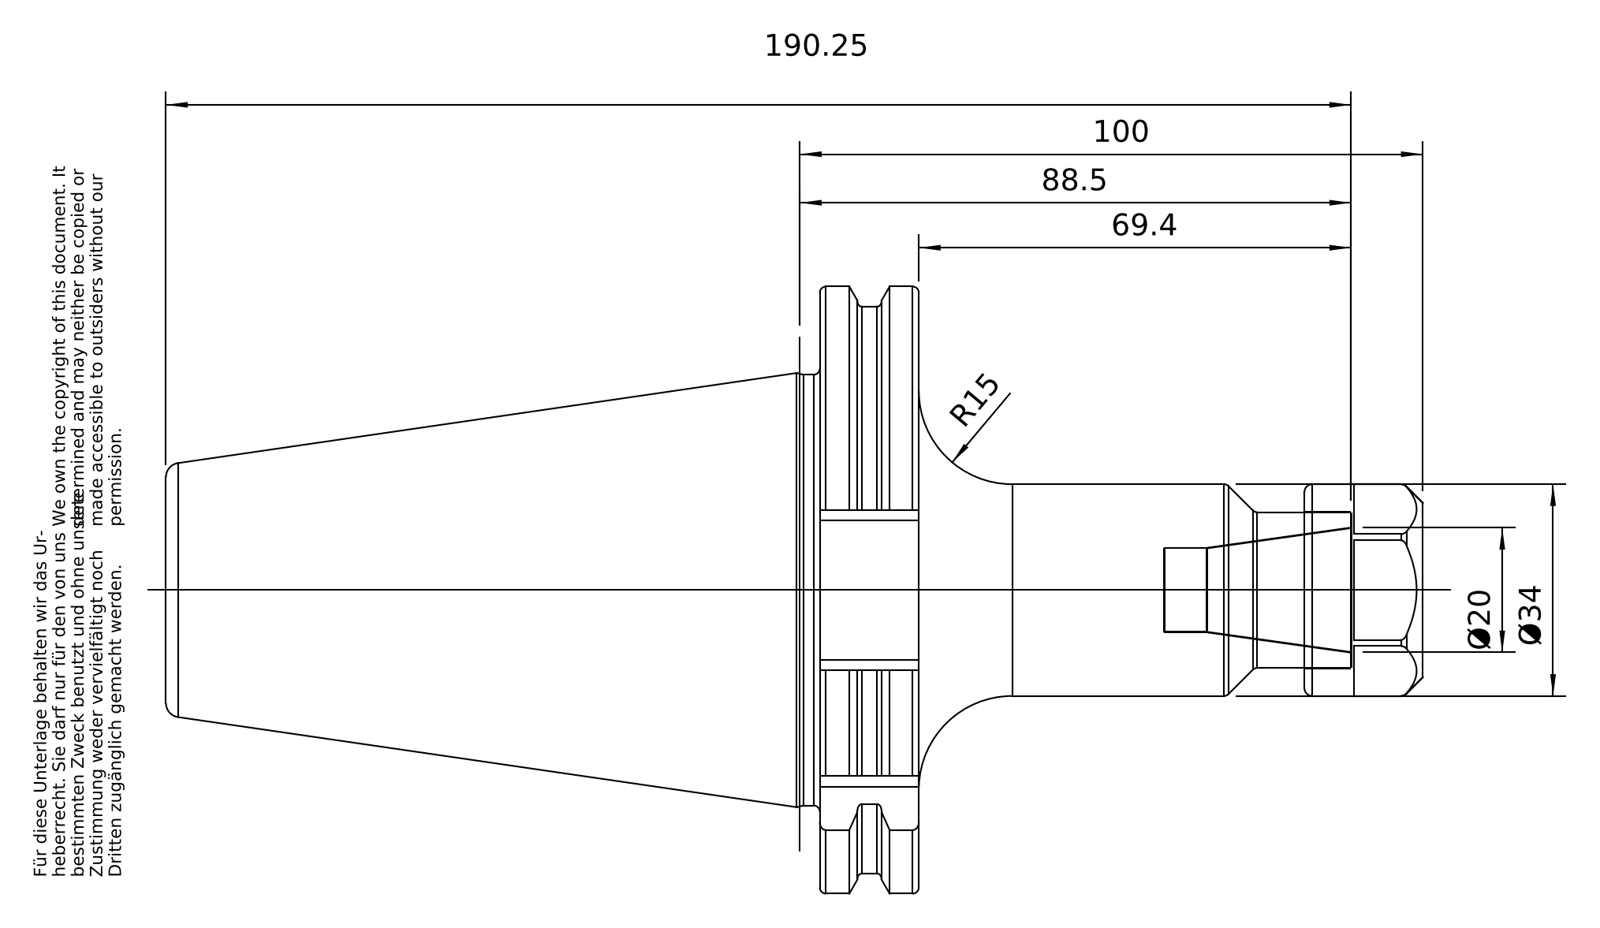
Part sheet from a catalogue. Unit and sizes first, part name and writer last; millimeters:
Units: millimetres
Overall size (bounding box): 201.6 × 97.47 × 94
Round holes (diameter × count): ⌀13.5 ×1, ⌀20.75 ×1, ⌀25.01 ×1, ⌀25.7 ×1
Round bosses / shafts (diameter × count): ⌀91 ×1, ⌀69.15 ×1, ⌀34 ×1, ⌀25 ×1, ⌀24.01 ×1
Partial cylindrical surfaces — rounded edges, fillets, slot ends (radius × count): R1.75 ×5, R48.74 ×1
Main face-to-face distances: 15.85, 77.8, 61.95, 30, 96.8, 80.95, 19, 104.8, 120.65, 182.6
Volume: 410 548 mm³ · Surface area: 53 607 mm²
Bodies: 2 solids, 129 faces (29 planar, 32 cylindrical, 68 other)
Part name (STEP PRODUCT): 50-321-20; 83-912-20; 50-321-20_ASM
STEP written by: PRO/ENGINEER BY PARAMETRIC TECHNOLOGY CORPORATION, 2010430 (CONFIG_CONTROL_DESIGN)
